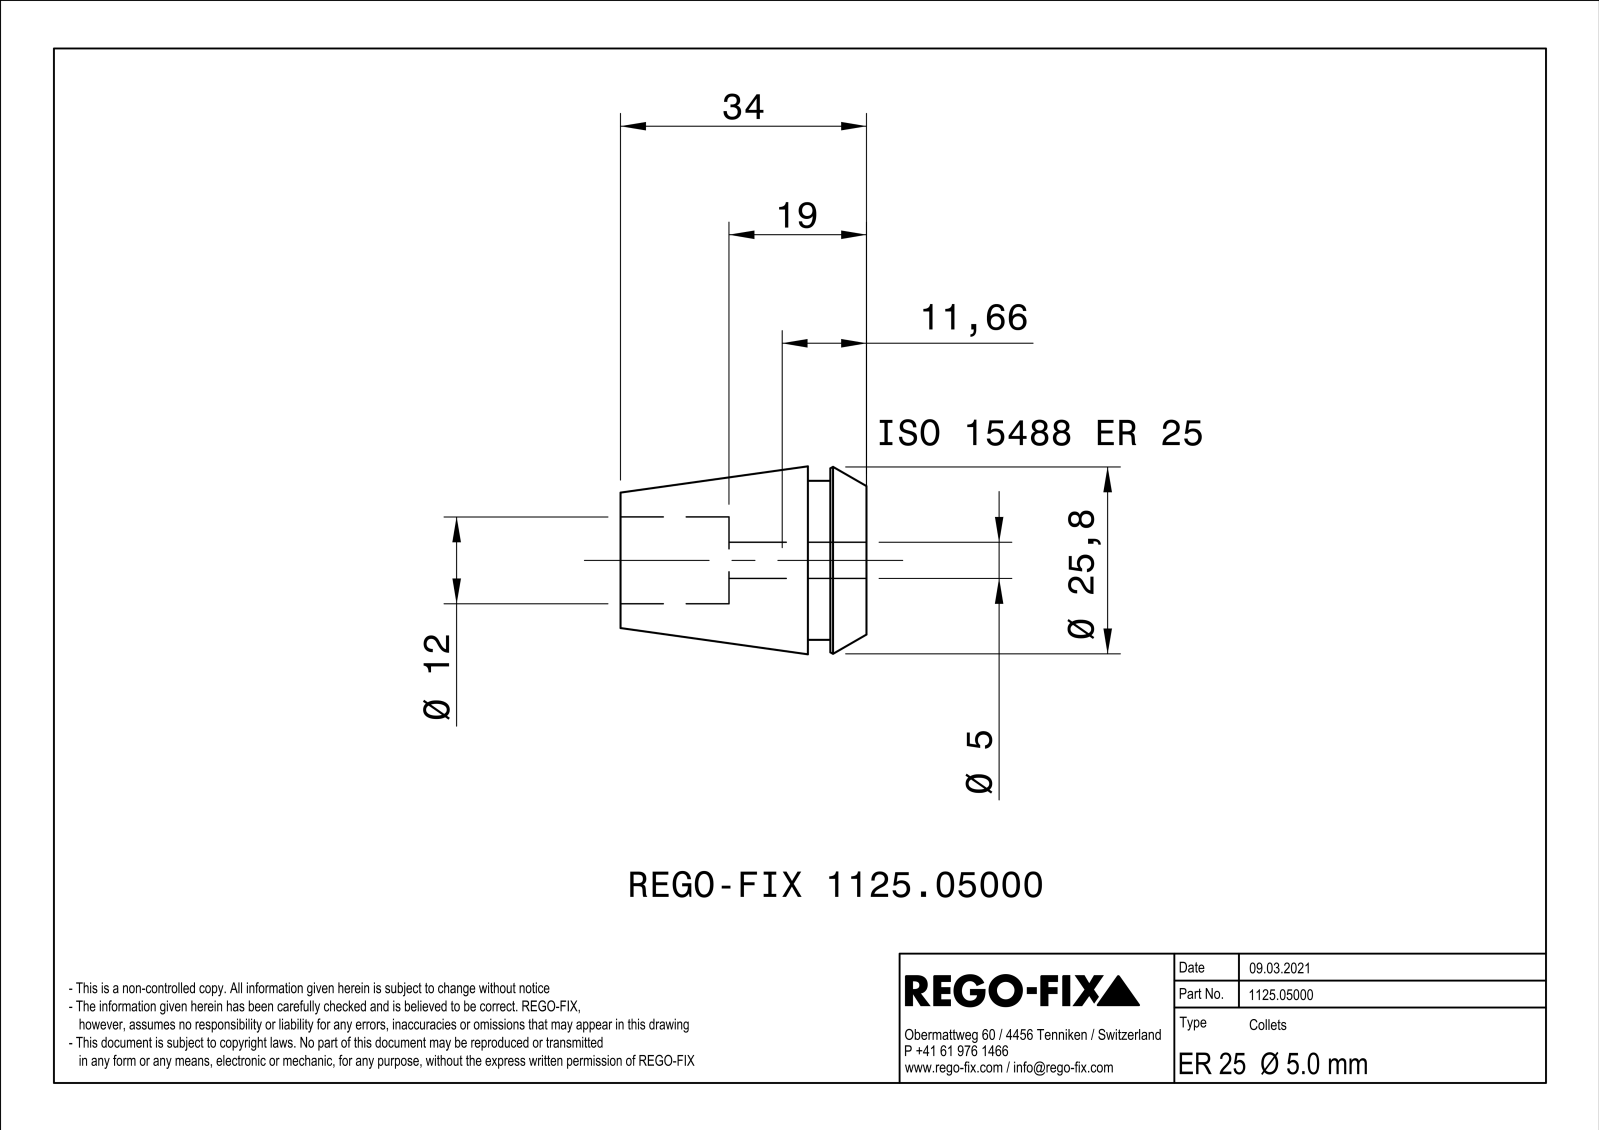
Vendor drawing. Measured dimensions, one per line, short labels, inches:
name: NOCUT
written by: SIEMENS PLM Software Solid Edge ST10 (AUTOMOTIVE_DESIGN)
unit: in
bodies: 1 solid, 256 faces (88 planar, 48 cylindrical, 120 other)
size: 1.339 × 1.023 × 1.023
volume: 0.566 in³; area: 14.03 in²
holes: 1× ⌀0.472
bosses: 1× ⌀0.866
rounds: 12× R0.016, 1× R0.098
face distances: 0.031, 0.032, 0.031, 0.319, 1.339, 1.02, 0.197, 0.122, 1.142, 0.748
